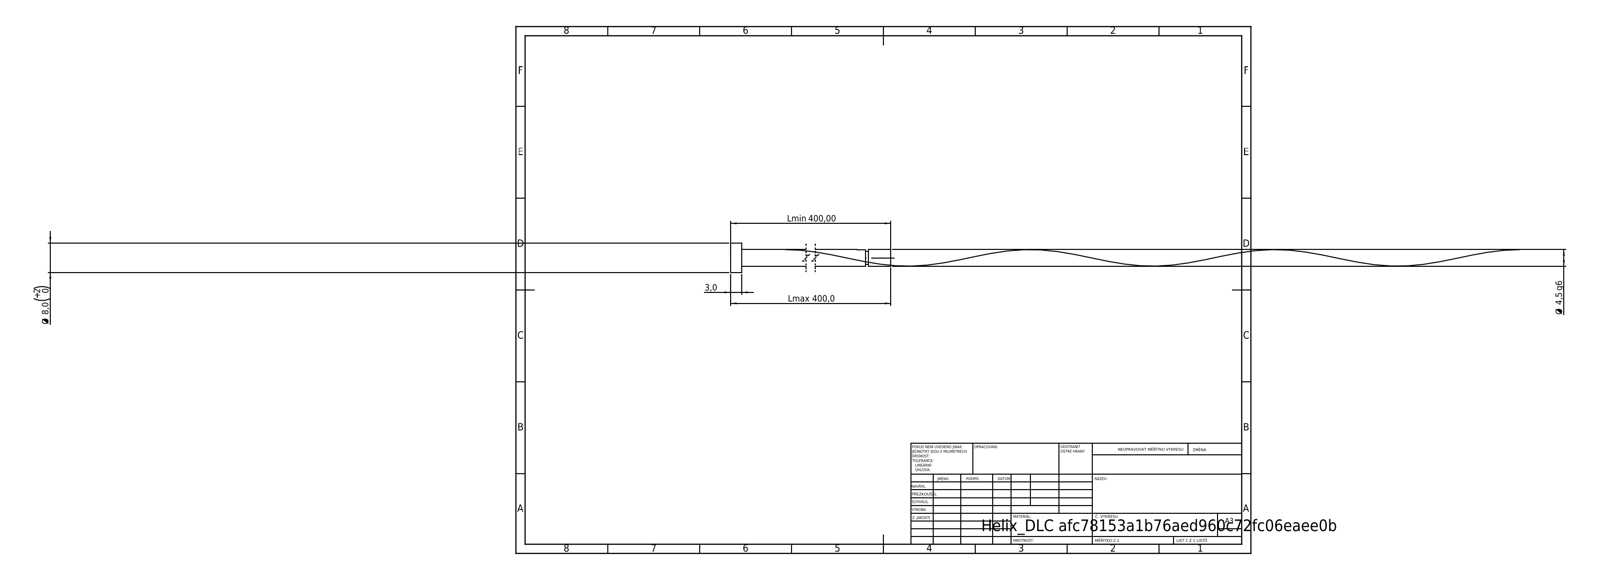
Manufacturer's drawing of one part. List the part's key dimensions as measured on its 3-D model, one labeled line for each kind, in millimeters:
STEP written by: SolidWorks 2019 (CONFIG_CONTROL_DESIGN)
Units: millimetres
Bodies: 1 solid, 16 faces (6 planar, 9 cylindrical, 1 other)
Overall size (bounding box): 400 × 8 × 8
Volume: 7 813 mm³ · Surface area: 7 770 mm²
Round bosses / shafts (diameter × count): ⌀8 ×1, ⌀4.5 ×1, ⌀3.6 ×1
Main face-to-face distances: 3, 400, 397, 393.94, 390.94, 6.06, 393.04, 390.04, 0.9, 6.96
